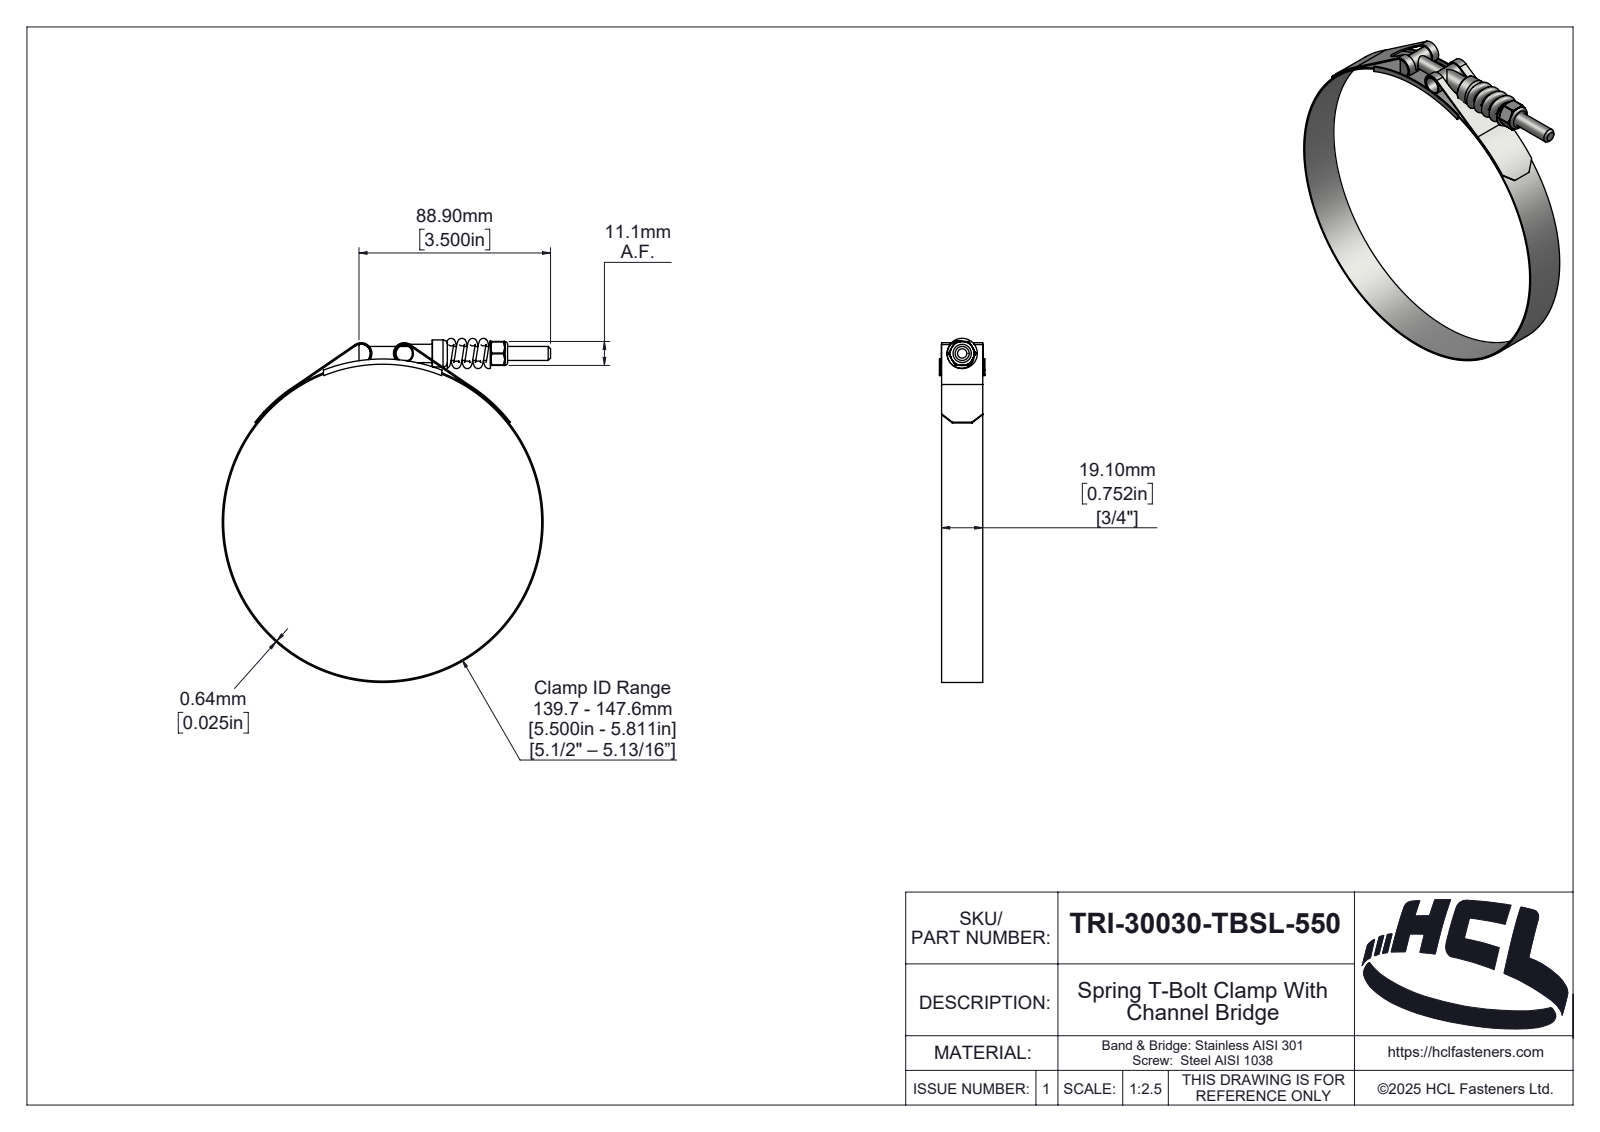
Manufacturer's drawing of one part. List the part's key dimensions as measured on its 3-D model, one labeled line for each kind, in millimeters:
Part name (STEP PRODUCT): TRI-30030-TBSL-550
STEP written by: SolidWorks 2025 (AUTOMOTIVE_DESIGN)
Units: millimetres
Bodies: 7 solids, 332 faces (48 planar, 122 cylindrical, 162 other)
Overall size (bounding box): 159.63 × 153.34 × 21.1
Volume: 14 239 mm³ · Surface area: 31 936 mm²
Round holes (diameter × count): ⌀5.4 ×1, ⌀6.35 ×1, ⌀6.5 ×1, ⌀7.52 ×1, ⌀147.6 ×1
Round bosses / shafts (diameter × count): ⌀8.52 ×2, ⌀148.88 ×1, ⌀12.52 ×1
Partial cylindrical surfaces — rounded edges, fillets, slot ends (radius × count): R0.39 ×6, R0.5 ×2, R4.36 ×2, R5 ×2, R0.59 ×1, R2.42 ×1, R3.03 ×1, R3.19 ×1
Main face-to-face distances: 0.64, 19.1, 1, 20.1, 20.46, 0.36, 19.46, 21.1, 61, 11.11
Hole centre spacings: 78.8
